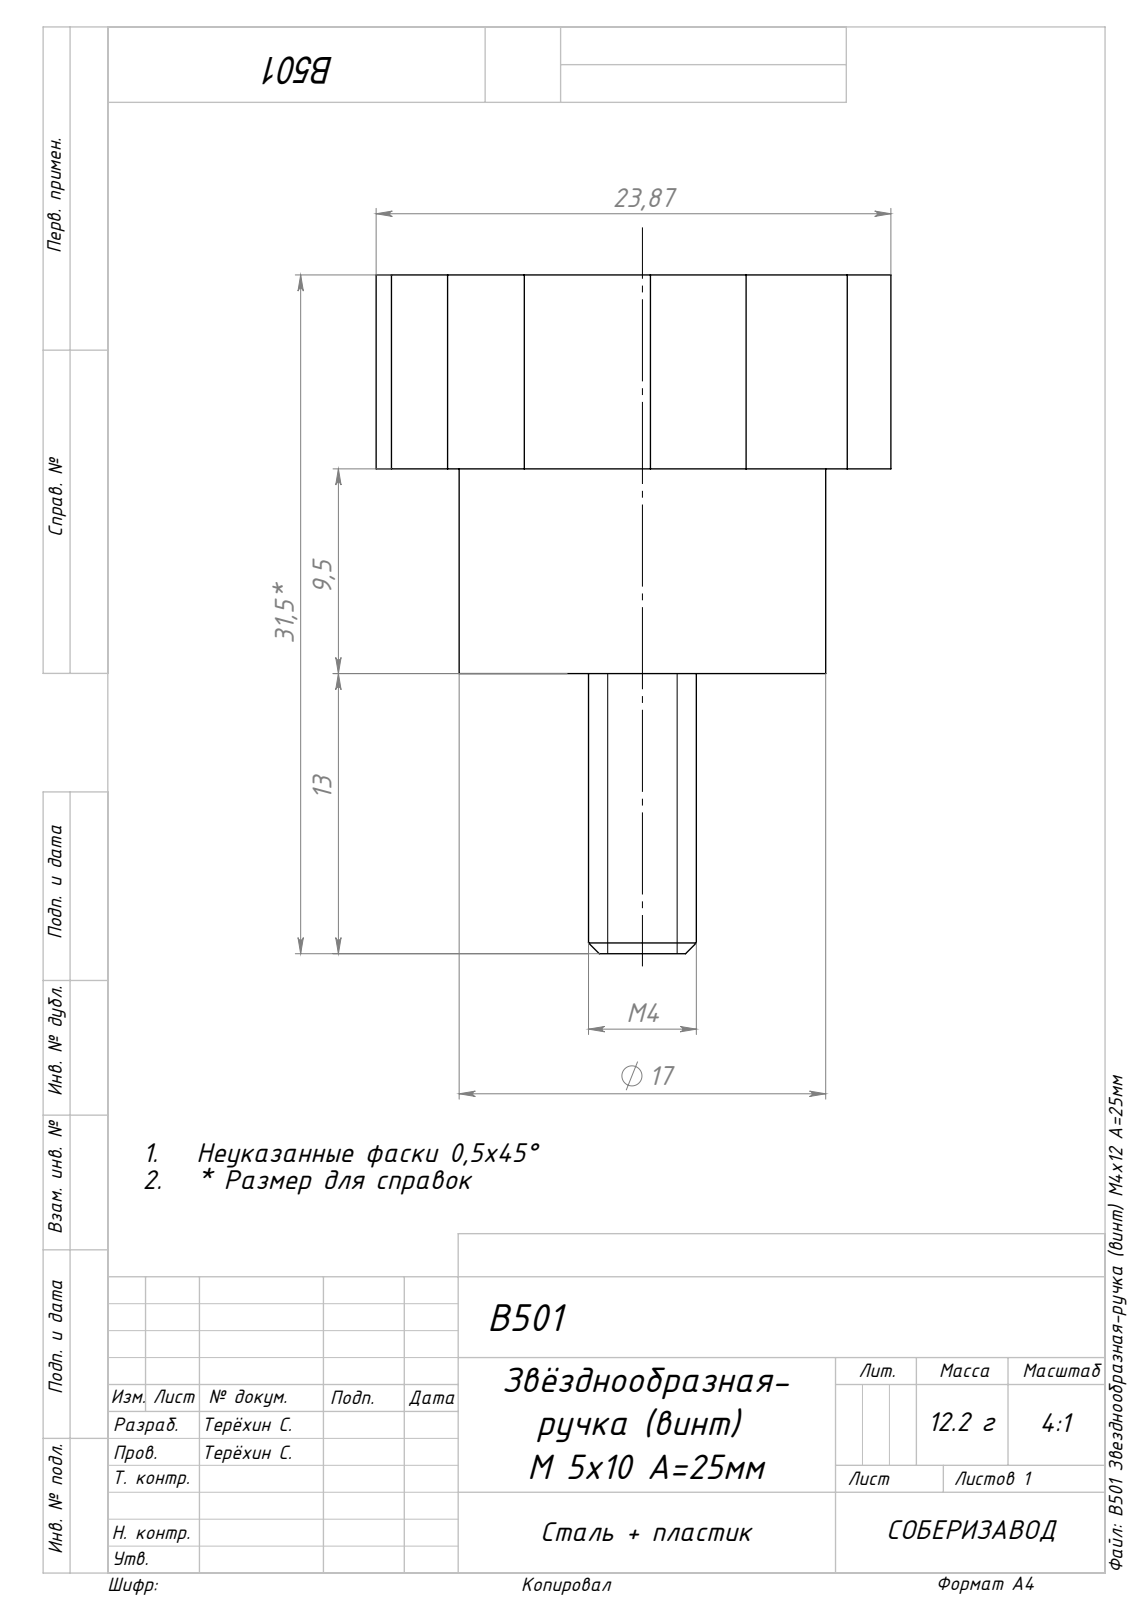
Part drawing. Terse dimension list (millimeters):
name: Сборка1; B501 Звезднообразная-ручка (винт) М4х12 А=25мм_00
written by: SolidWorks 2025 (AUTOMOTIVE_DESIGN)
unit: mm
bodies: 2 solids, 45 faces (13 planar, 30 cylindrical, 2 other)
size: 31.5 × 24.28 × 23.87
volume: 6 002 mm³; area: 2 963 mm²
holes: 1× ⌀10
bosses: 1× ⌀17, 1× ⌀5
rounds: 7× R4, 7× R4.57, 6× R2
face distances: 9, 9.5, 18.5, 13, 22.5, 31.5
